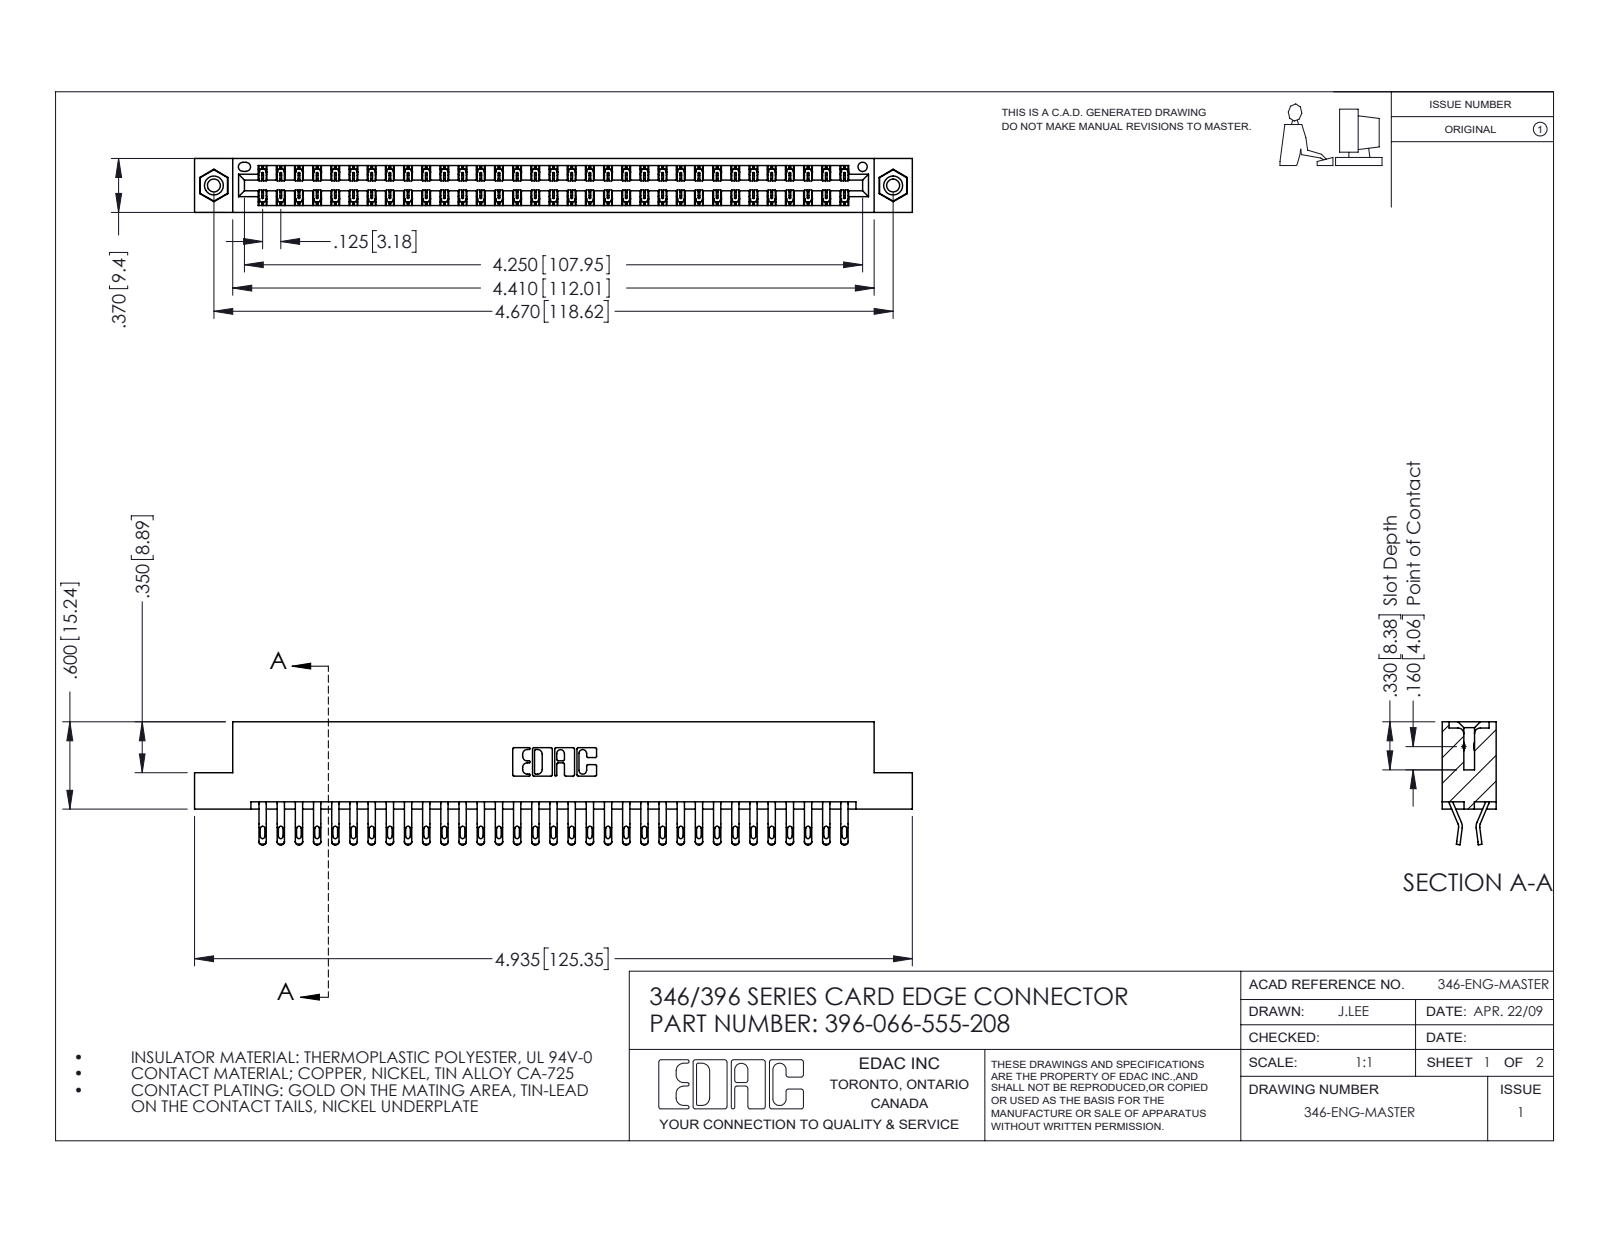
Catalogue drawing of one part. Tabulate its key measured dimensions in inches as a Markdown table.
| quantity | value |
| --- | --- |
| part name | 396-066-555-208; 345-292-001_555 Tail; 346 Part_Flush Mounting Lugs - 0.156 Dia-TI; 345-250-001_345-250-003-102 |
| STEP written by | SolidWorks 2016 (CONFIG_CONTROL_DESIGN) |
| units | inches |
| bodies | 69 solids, 4010 faces (2286 planar, 1708 cylindrical, 16 other) |
| overall size | 4.935 × 0.845 × 0.37 |
| volume | 0.753 in³ |
| surface area | 27.16 in² |
| round holes (diameter × count) | 0.089 × 2, 0.125 × 2, 0.156 × 2, 0.064 × 1 |
| round bosses / shafts (diameter × count) | 0.155 × 2 |
| partial cylindrical surfaces (radius × count) | 0.016 × 132, 0.02 × 132, 0.006 × 99, 0.01 × 22, 0.007 × 6, 0.031 × 6, 0.026 × 3, 0.01 × 2 |
| main face-to-face distances | 0.048, 0.322, 0.37, 0.25, 0.025, 0.072, 0.298, 0.275, 0.148, 0.222 |
| hole center spacings | 0.246, 4.462, 4.67 |
